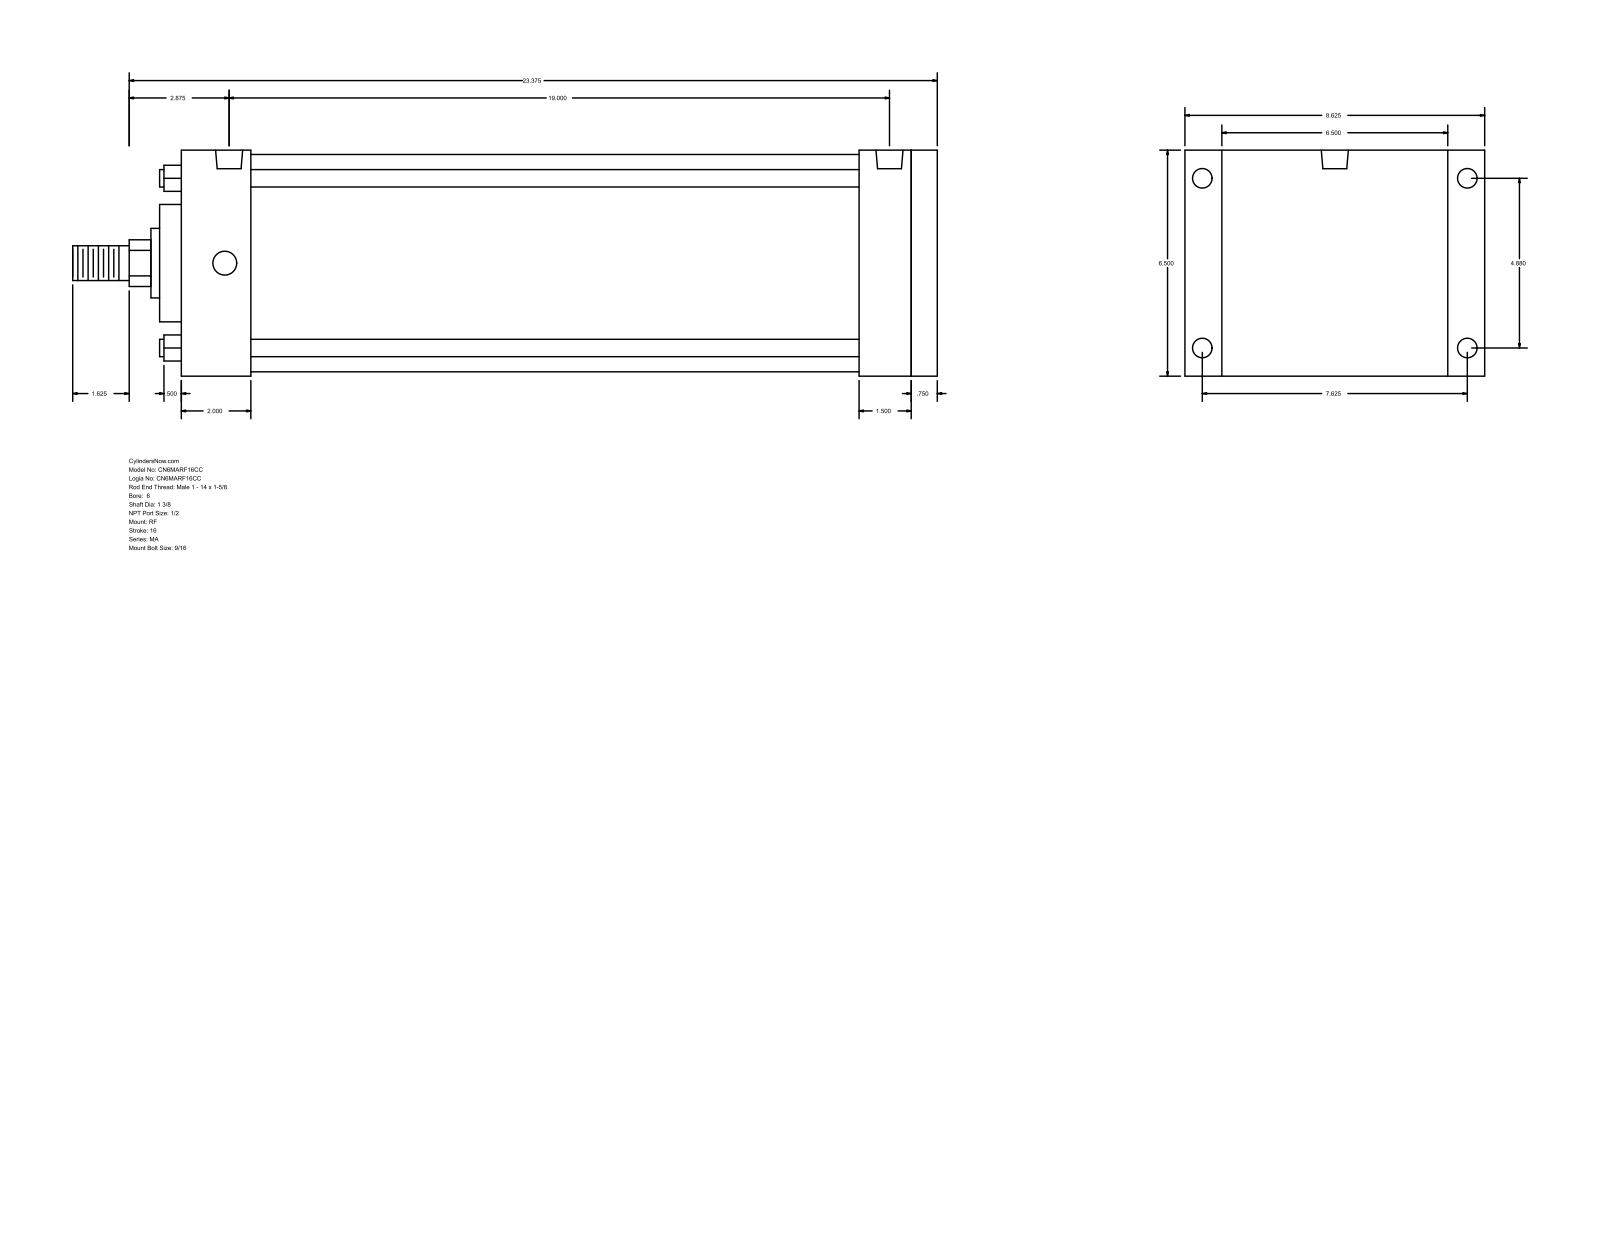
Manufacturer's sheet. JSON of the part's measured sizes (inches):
{"part_name": "MA_RF__0600_1.375", "step_written_by": "GSSL Pune (CONFIG_CONTROL_DESIGN)", "units": "inches", "bodies": {"solids": 0, "faces": 94, "planar": 65, "cylindrical": 29, "other": 0}, "overall_size": [25, 8.625, 6.5], "round_holes": [[0.563, 4], [0.687, 4], [0.778, 2]], "round_bosses_or_shafts": [[0.5, 4], [6.25, 1], [3.375, 1], [2, 1], [1.375, 1], [1, 1]], "partial_cylinders_radius": [[0.672, 1]], "face_to_face_distances": [6.5, 21.875, 21.125, 0.75, 2.25, 2, 19.125, 19.875, 19.625, 17.625], "hole_center_spacings": [4.88, 7.625, 9.053, 19.125, 0.125, 19]}
